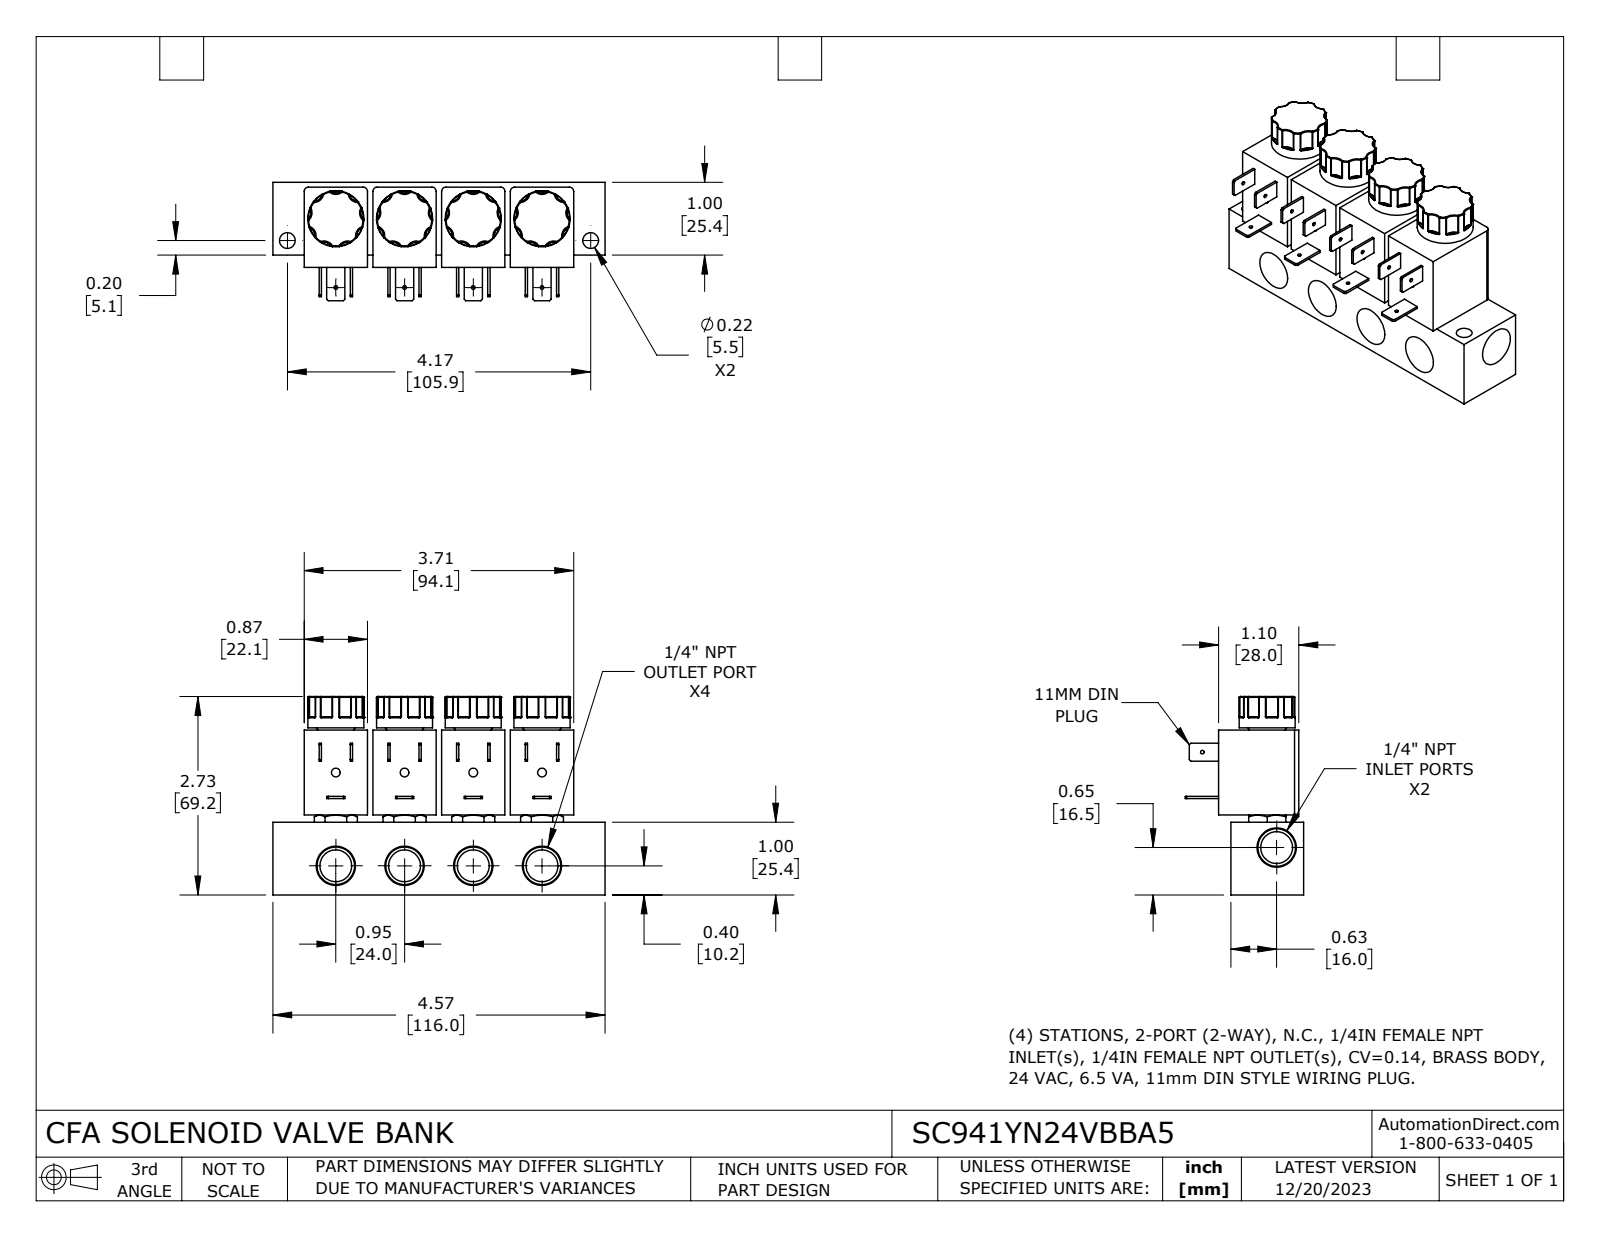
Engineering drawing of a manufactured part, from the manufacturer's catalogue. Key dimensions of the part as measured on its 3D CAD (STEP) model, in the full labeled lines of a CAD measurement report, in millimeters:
Part name (STEP PRODUCT): SC941YN24VBBA5
STEP written by: SolidWorks 2023 (CONFIG_CONTROL_DESIGN)
Units: millimetres
Bodies: 1 solid, 868 faces (192 planar, 184 cylindrical, 492 other)
Overall size (bounding box): 116 × 69.2 × 41.3
Volume: 150 500 mm³ · Surface area: 39 390 mm²
Round holes (diameter × count): ⌀1.3 ×5, ⌀11.1 ×5, ⌀3 ×4, ⌀5.5 ×2
Round bosses / shafts (diameter × count): ⌀19.6 ×4
Partial cylindrical surfaces — rounded edges, fillets, slot ends (radius × count): R0.3 ×72, R3.4 ×34, R1.5 ×8, R3.4 ×2
Main face-to-face distances: 25.4, 24, 29.7, 48, 46.1, 22.1, 4.3, 1.7, 23.7, 28
Hole centre spacings: 24, 32.6, 40.5, 24, 48, 48, 72, 40.5
